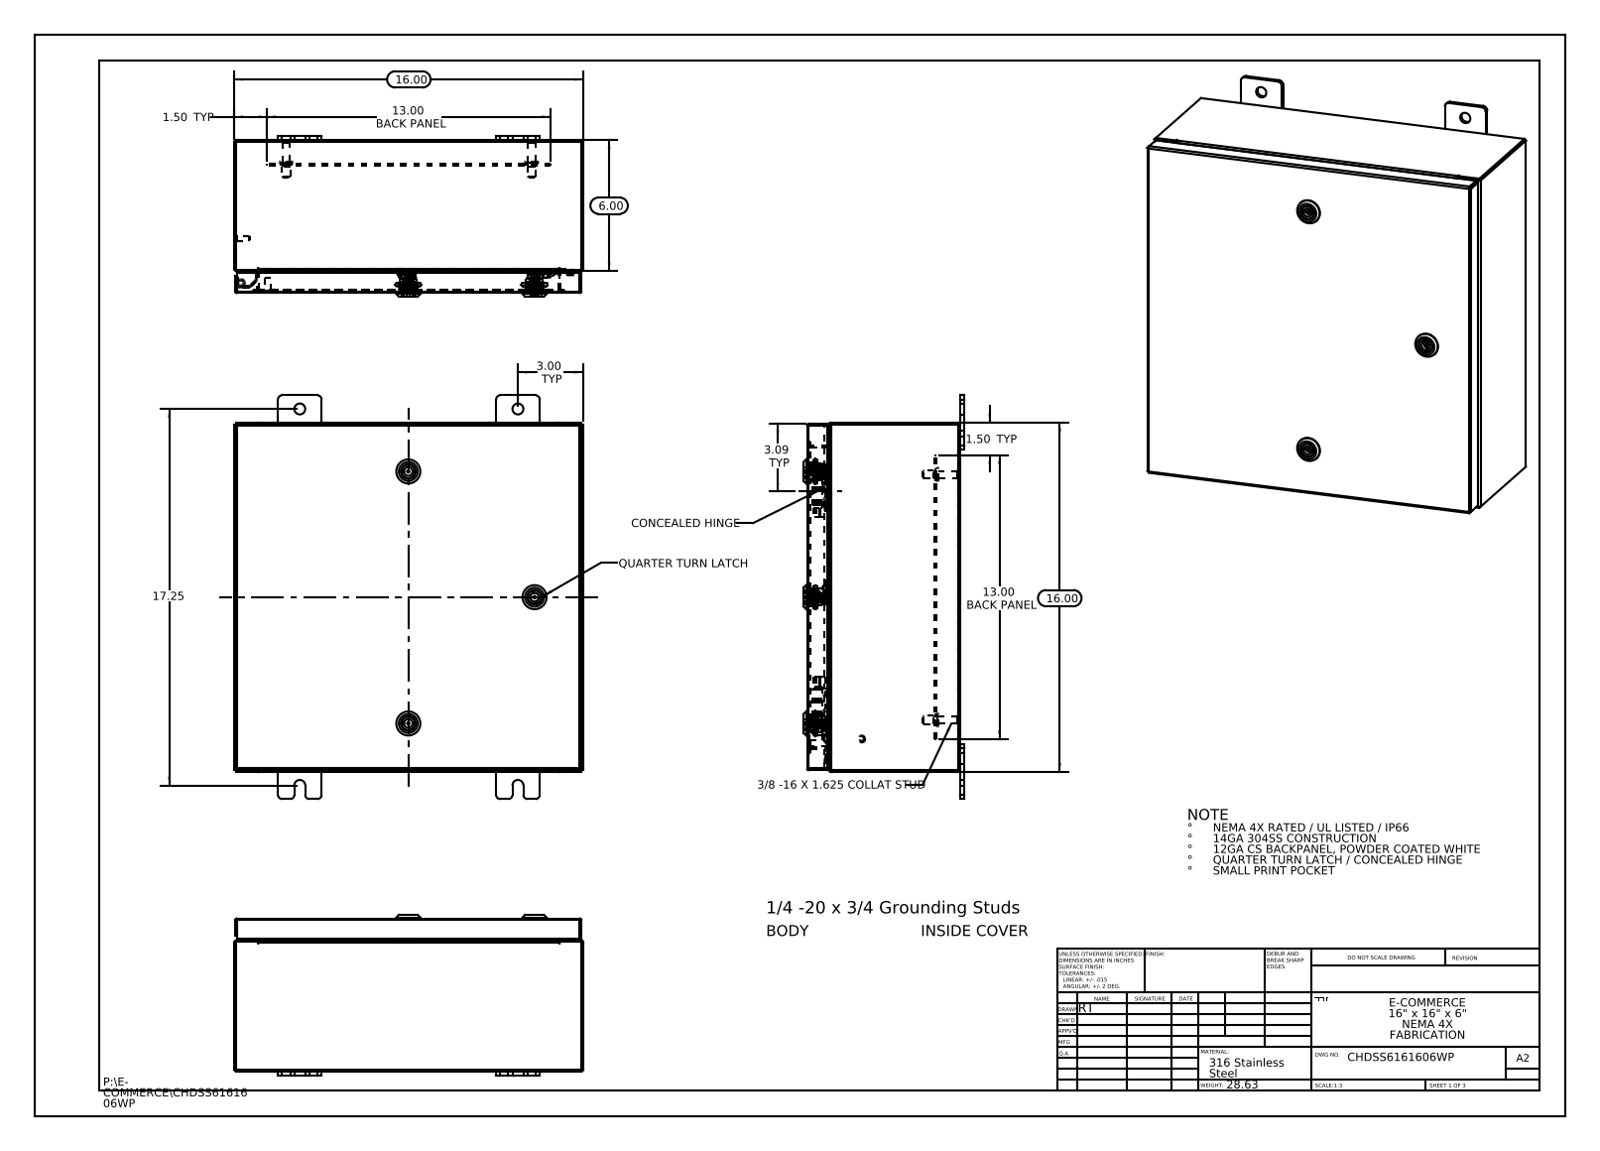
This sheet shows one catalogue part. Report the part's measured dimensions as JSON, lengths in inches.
{"part_name": "HW-CLH-E5-8004_Cam-232112-U-Industrilas; CHDSS6161606WP Mounting Feet; Screw-221320-IB-Industrilas_Screw-221320-IB-Industrilas; Concealed Hinge enclosure side (+8 more)", "step_written_by": "SolidWorks 2013 (CONFIG_CONTROL_DESIGN)", "units": "inches", "bodies": {"solids": 37, "faces": 2966, "planar": 938, "cylindrical": 930, "other": 1098}, "overall_size": [18.5, 16, 7.356], "volume_in3": 102.6, "surface_area_in2": 2580, "round_holes": [[0.5, 8], [0.136, 4], [0.197, 3], [0.394, 3], [0.4, 3], [0.63, 3], [0.787, 3], [0.211, 1]], "round_bosses_or_shafts": [[0.236, 5], [0.625, 4], [0.375, 4], [0.33, 4], [1.102, 3], [0.78, 3], [0.626, 3], [0.61, 3]], "partial_cylinders_radius": [[0.006, 99], [0.118, 99], [0.028, 36], [0.19, 24], [0.013, 18], [0.088, 18], [0.02, 12], [0.197, 12]], "face_to_face_distances": [0.075, 15.925, 0.074, 7.01, 6.935, 6.936, 6.861, 15.85, 16, 1], "hole_center_spacings": [0.688, 1.858, 3.065, 5.627, 9.687, 10, 11.25, 11.25]}
